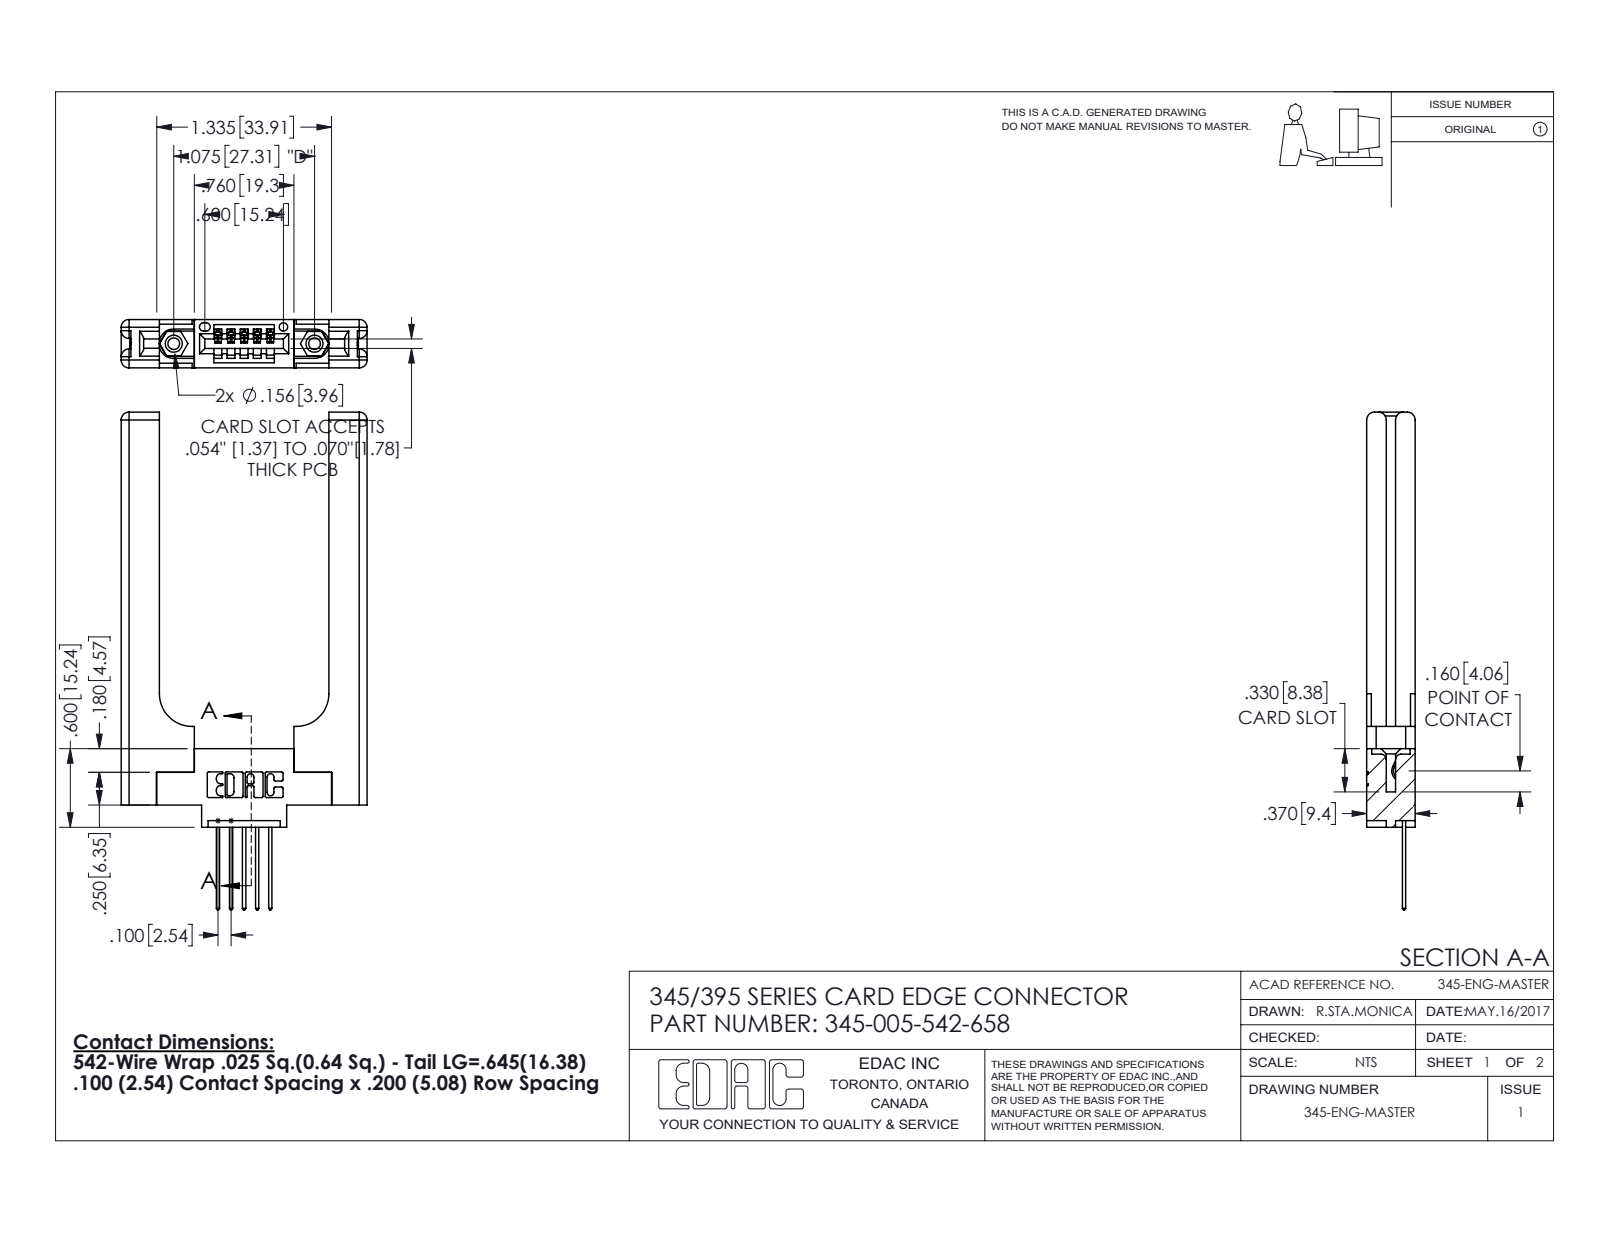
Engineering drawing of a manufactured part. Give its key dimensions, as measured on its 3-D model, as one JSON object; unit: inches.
{"part_name": "345-220-058_345-220-058; 345-005-542-658; 345-292-001_345-293-142; 345-250-001_345-250-001-102 (+1 more)", "step_written_by": "SolidWorks 2016 (CONFIG_CONTROL_DESIGN)", "units": "inches", "bodies": {"solids": 10, "faces": 676, "planar": 432, "cylindrical": 184, "other": 60}, "overall_size": [3.802, 1.879, 0.37], "volume_in3": 0.771, "surface_area_in2": 16.25, "round_holes": [[0.089, 2], [0.125, 2], [0.156, 2], [0.064, 1]], "round_bosses_or_shafts": [[0.155, 2]], "partial_cylinders_radius": [[0.01, 22], [0.06, 16], [0.006, 10], [0.01, 10], [0.007, 6], [0.031, 6], [0.026, 3], [0.03, 2]], "face_to_face_distances": [0.37, 0.15, 0.22, 0.072, 1.296, 0.148, 0.077, 0.298, 0.071, 0.292], "hole_center_spacings": [0.27, 0.847, 1.075]}
